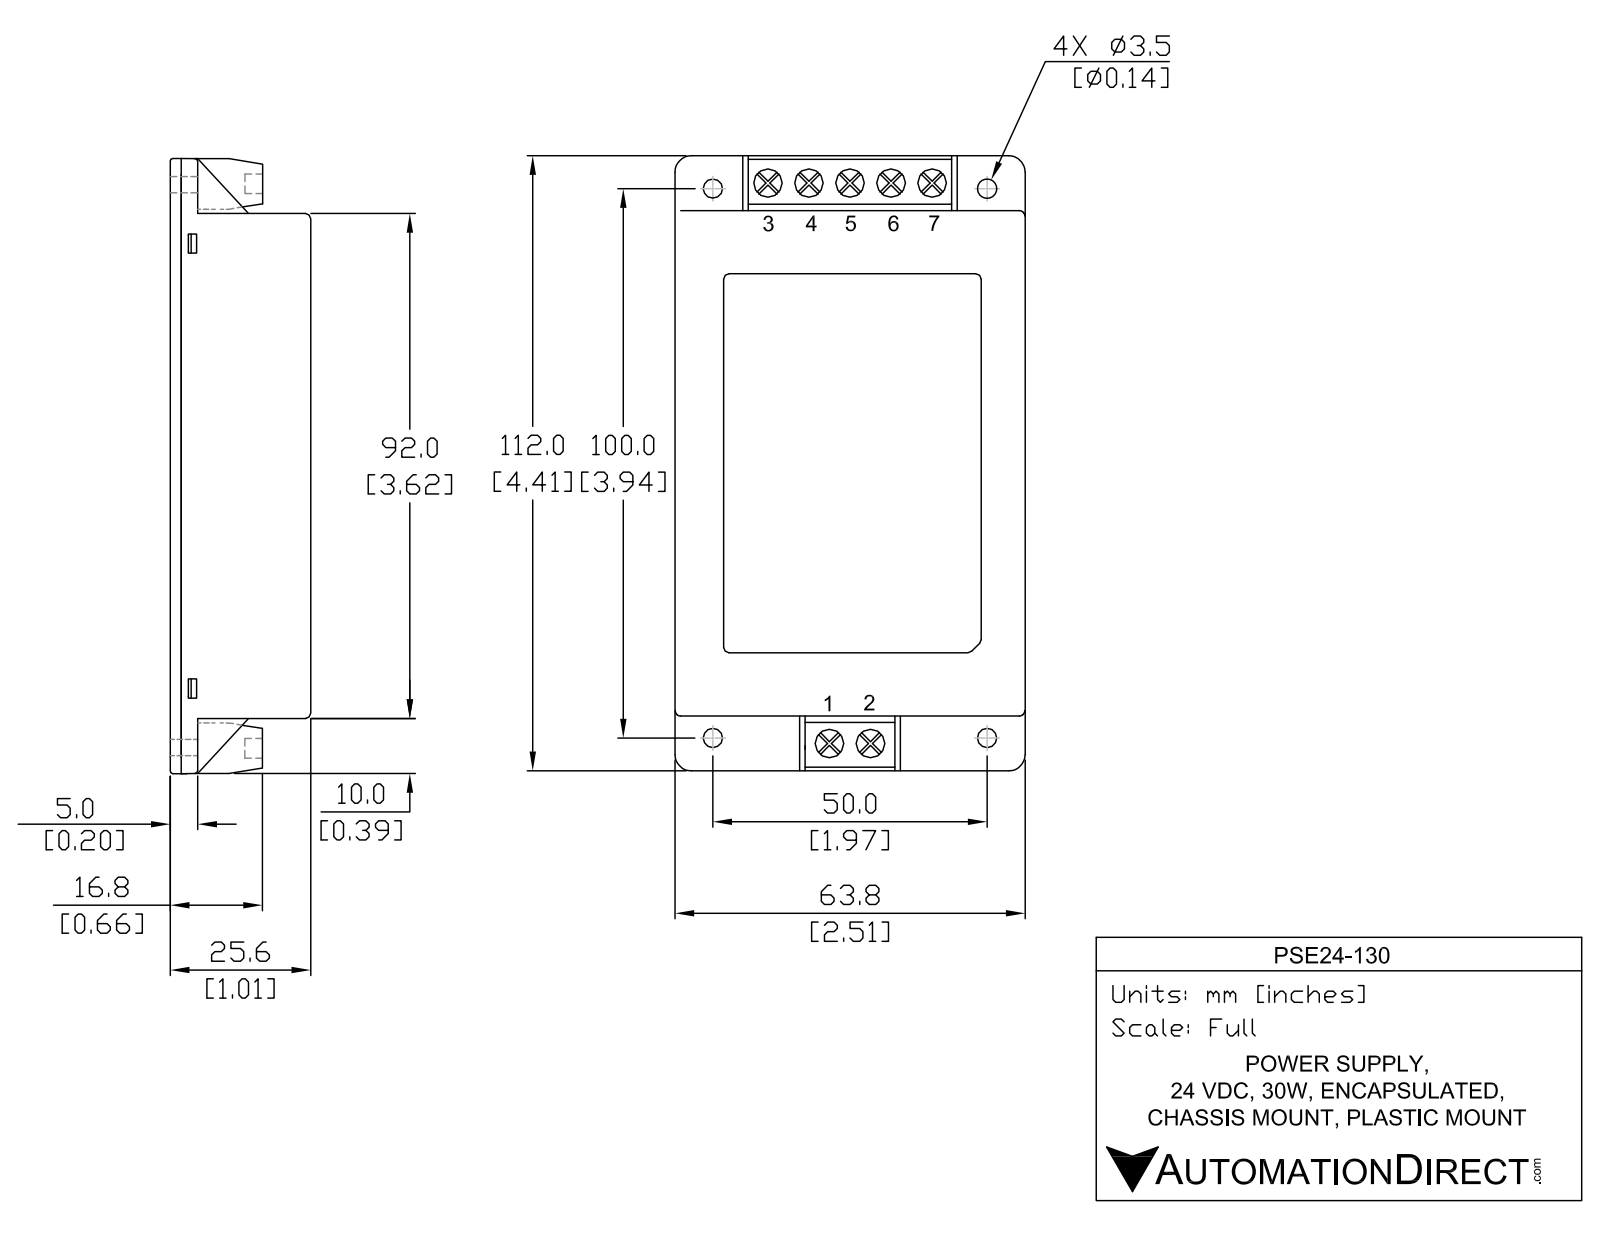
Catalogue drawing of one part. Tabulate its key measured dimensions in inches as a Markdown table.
| quantity | value |
| --- | --- |
| part name | PSE24-130 |
| STEP written by | SolidWorks 2011 (CONFIG_CONTROL_DESIGN) |
| units | inches |
| bodies | 2 solids, 374 faces (246 planar, 62 cylindrical, 66 other) |
| overall size | 4.41 × 2.51 × 1.01 |
| volume | 9.834 in³ |
| surface area | 60.49 in² |
| round holes (diameter × count) | 0.2 × 7, 0.14 × 4 |
| partial cylindrical surfaces (radius × count) | 0.03 × 20, 0.125 × 4 |
| main face-to-face distances | 0.078, 0.08, 0.93, 1.008, 0.928, 1.01, 0.932, 2.51, 3.62, 0.015 |
| hole center spacings | 0.26, 0.52, 0.26, 0.856, 1.116, 1.97, 3.94, 4.015 |
